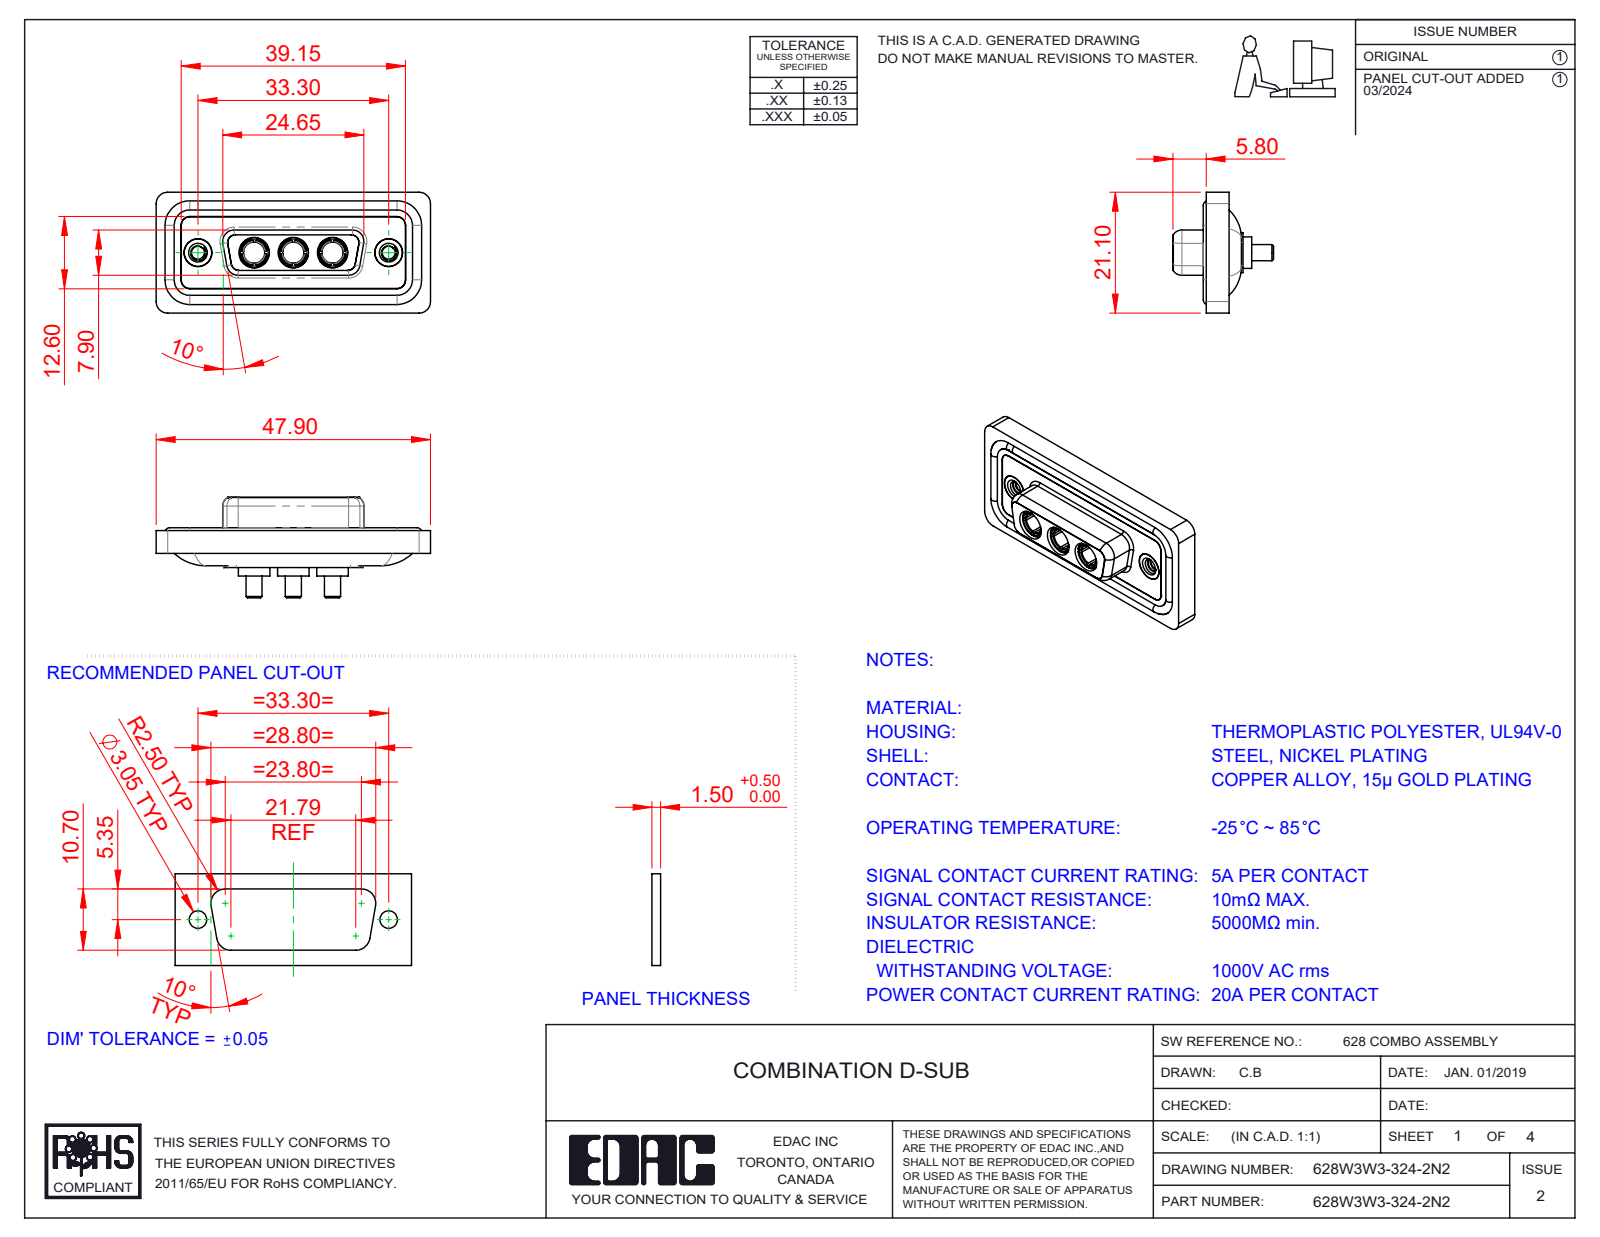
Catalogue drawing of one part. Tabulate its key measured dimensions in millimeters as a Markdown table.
| quantity | value |
| --- | --- |
| part name | 628Combo Shell Rear_15 Contacts; 628Combo Waterproof Housing_15 Contacts; 628W3W3-324-2N2; 628Combo Housing_3W3 (+3 more) |
| STEP written by | SolidWorks 2023 (CONFIG_CONTROL_DESIGN) |
| units | millimeters |
| bodies | 13 solids, 608 faces (192 planar, 257 cylindrical, 159 other) |
| overall size | 47.9 × 21.1 × 17.55 |
| volume | 6 026 mm³ |
| surface area | 9 739 mm² |
| round holes (diameter × count) | 4.85 × 5, 3.7 × 3, 5.3 × 3, 2.26 × 2, 4 × 2, 4.05 × 2, 5 × 2 |
| round bosses / shafts (diameter × count) | 1.6 × 4, 5.5 × 3, 5.2 × 3, 4.96 × 3, 4.75 × 3, 3.75 × 3, 2.8 × 3, 4.95 × 2 |
| partial cylindrical surfaces (radius × count) | 1.5 × 22, 2 × 20, 1.35 × 12, 1.6 × 8, 0.25 × 4, 0.5 × 4, 0.6 × 4, 0.65 × 4 |
| main face-to-face distances | 0.4, 1.8, 1.6, 0.5, 7.45, 1.1, 2.9, 5.65, 7.05, 6.6 |
| hole center spacings | 6.85, 9.8, 16.65, 23.5, 13.7, 33.3 |
